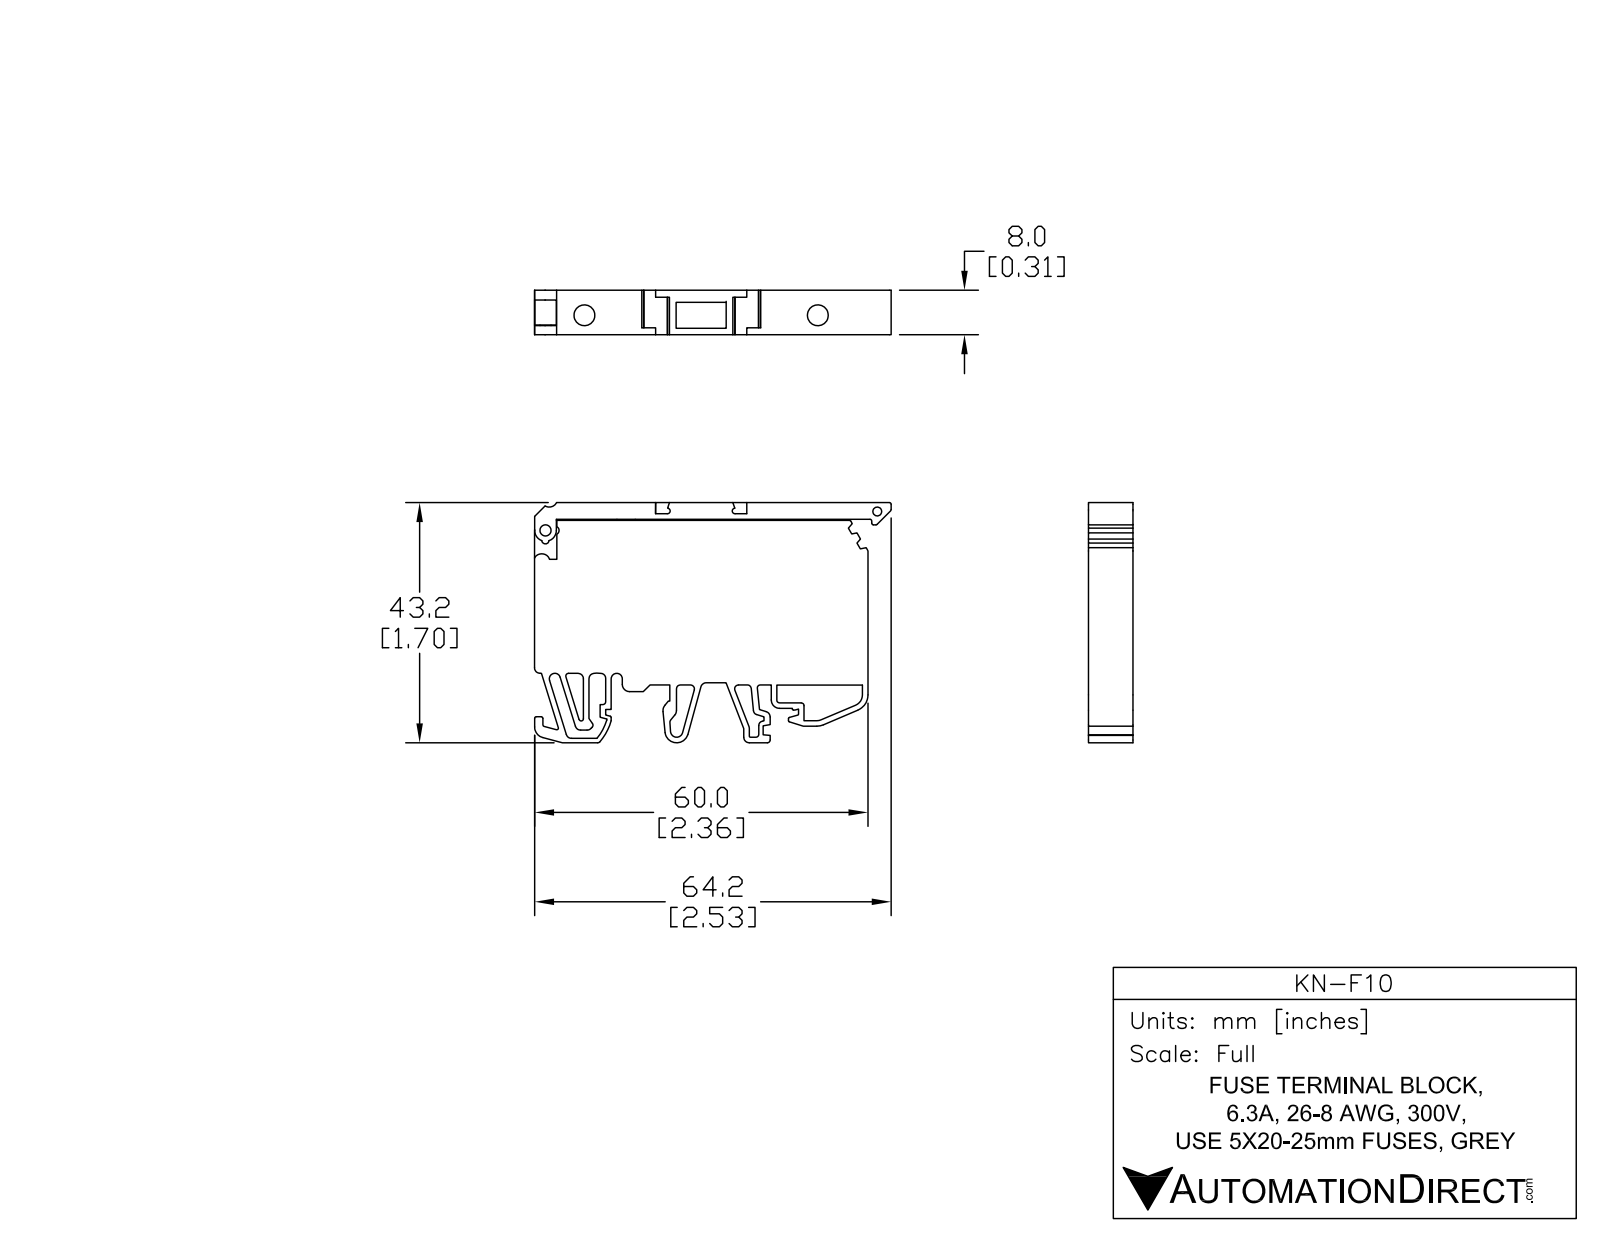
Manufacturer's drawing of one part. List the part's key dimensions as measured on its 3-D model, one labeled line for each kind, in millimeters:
Part name (STEP PRODUCT): KN-F10
STEP written by: SolidWorks 2014 (AUTOMOTIVE_DESIGN)
Units: millimetres
Bodies: 2 solids, 245 faces (142 planar, 103 cylindrical, 0 other)
Overall size (bounding box): 64.18 × 43.2 × 8
Volume: 16 117 mm³ · Surface area: 8 946 mm²
Round holes (diameter × count): ⌀3.75 ×2, ⌀1.6 ×1, ⌀2 ×1, ⌀3.3 ×1
Partial cylindrical surfaces — rounded edges, fillets, slot ends (radius × count): R0.3 ×12, R1 ×11, R0.5 ×9, R0.2 ×7, R0.5 ×4, R0.7 ×4, R1.5 ×4, R2 ×4
Main face-to-face distances: 8, 3, 3.2, 1, 60, 2, 32.82, 29.62, 29.82, 4
Hole centre spacings: 7.67, 34.54, 42, 59.8
